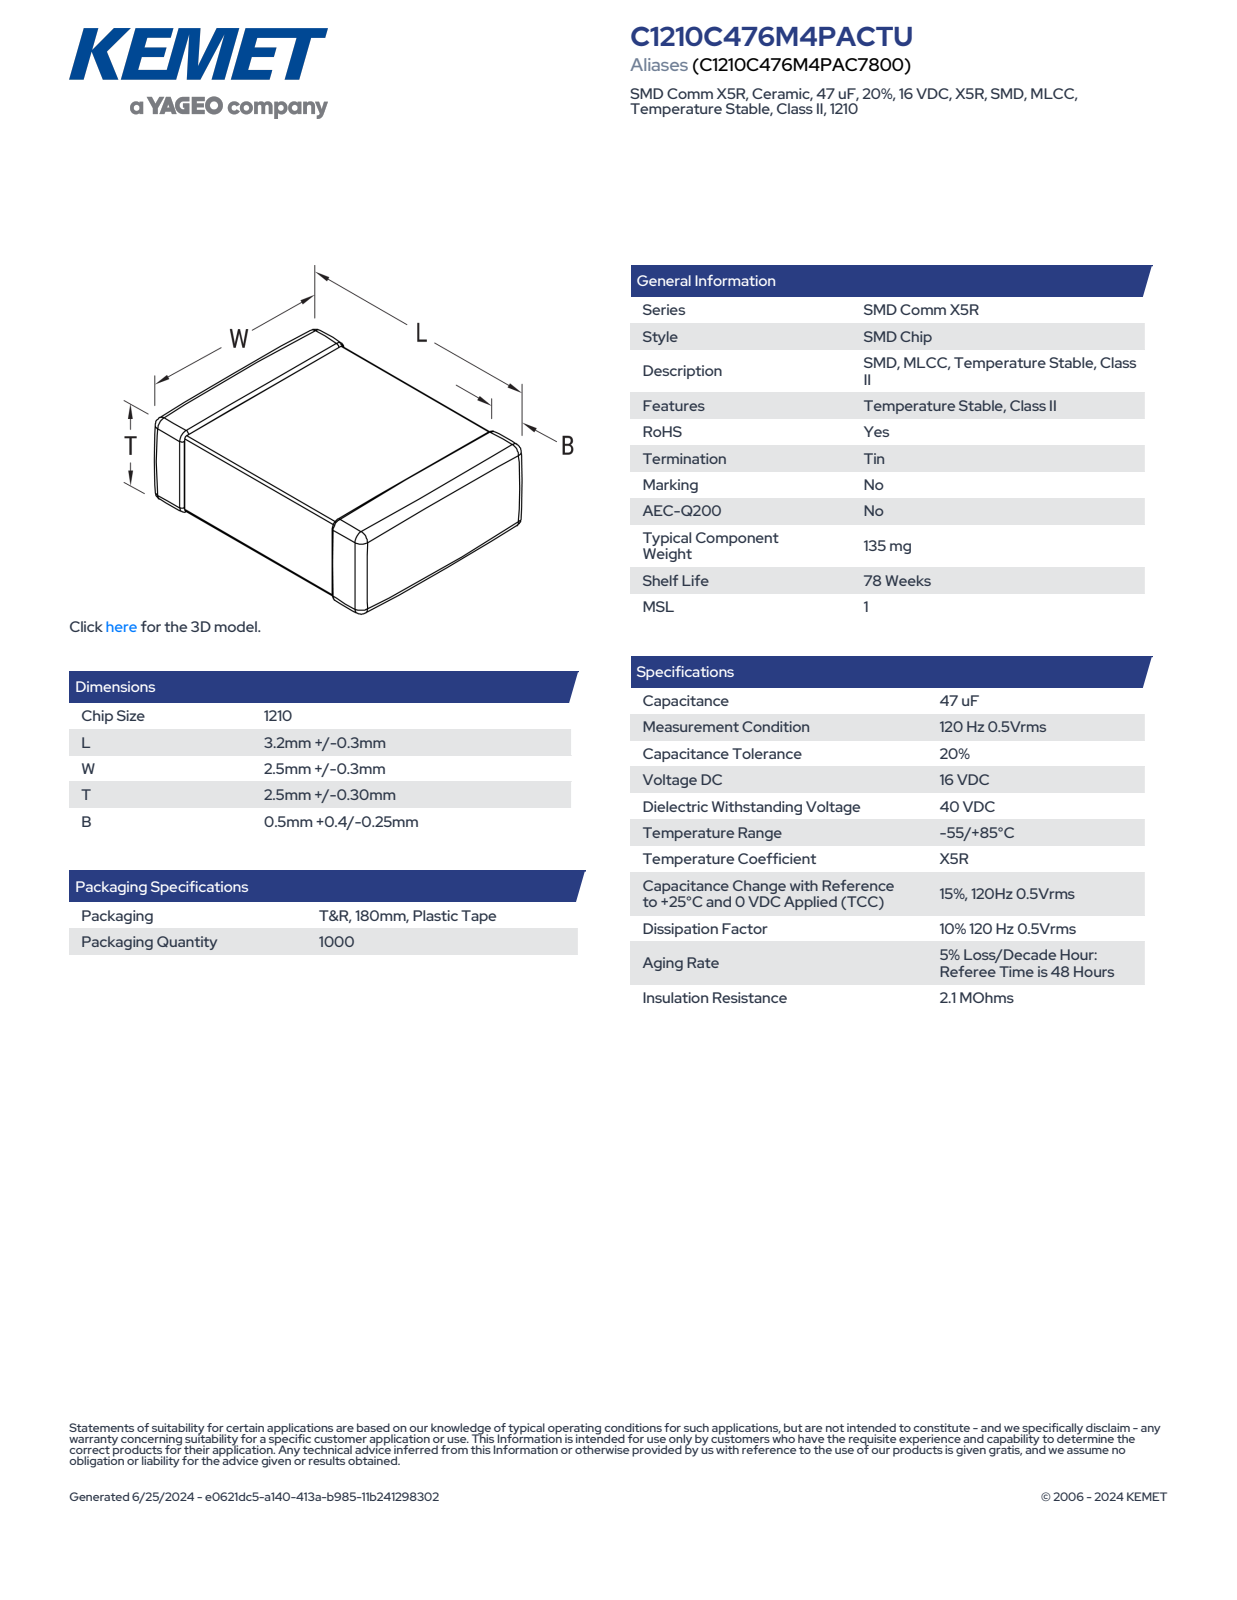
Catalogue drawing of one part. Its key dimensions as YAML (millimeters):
part_name: "CCS_CCSTDNOS_1210_L3.5W2.8T2.8B0.9"
step_written_by: "SolidWorks 2014 (AUTOMOTIVE_DESIGN)"
units: millimeters
bodies: {solids: 4, faces: 125, planar: 71, cylindrical: 38, other: 16}
overall_size: [3.5, 2.8, 2.8]
volume: 26
surface_area: 54
face_to_face_distances: [2.74, 2.68, 2.8, 3.5, 2.75, 2.69, 1.3, 1.44, 1.36, 1.38]
